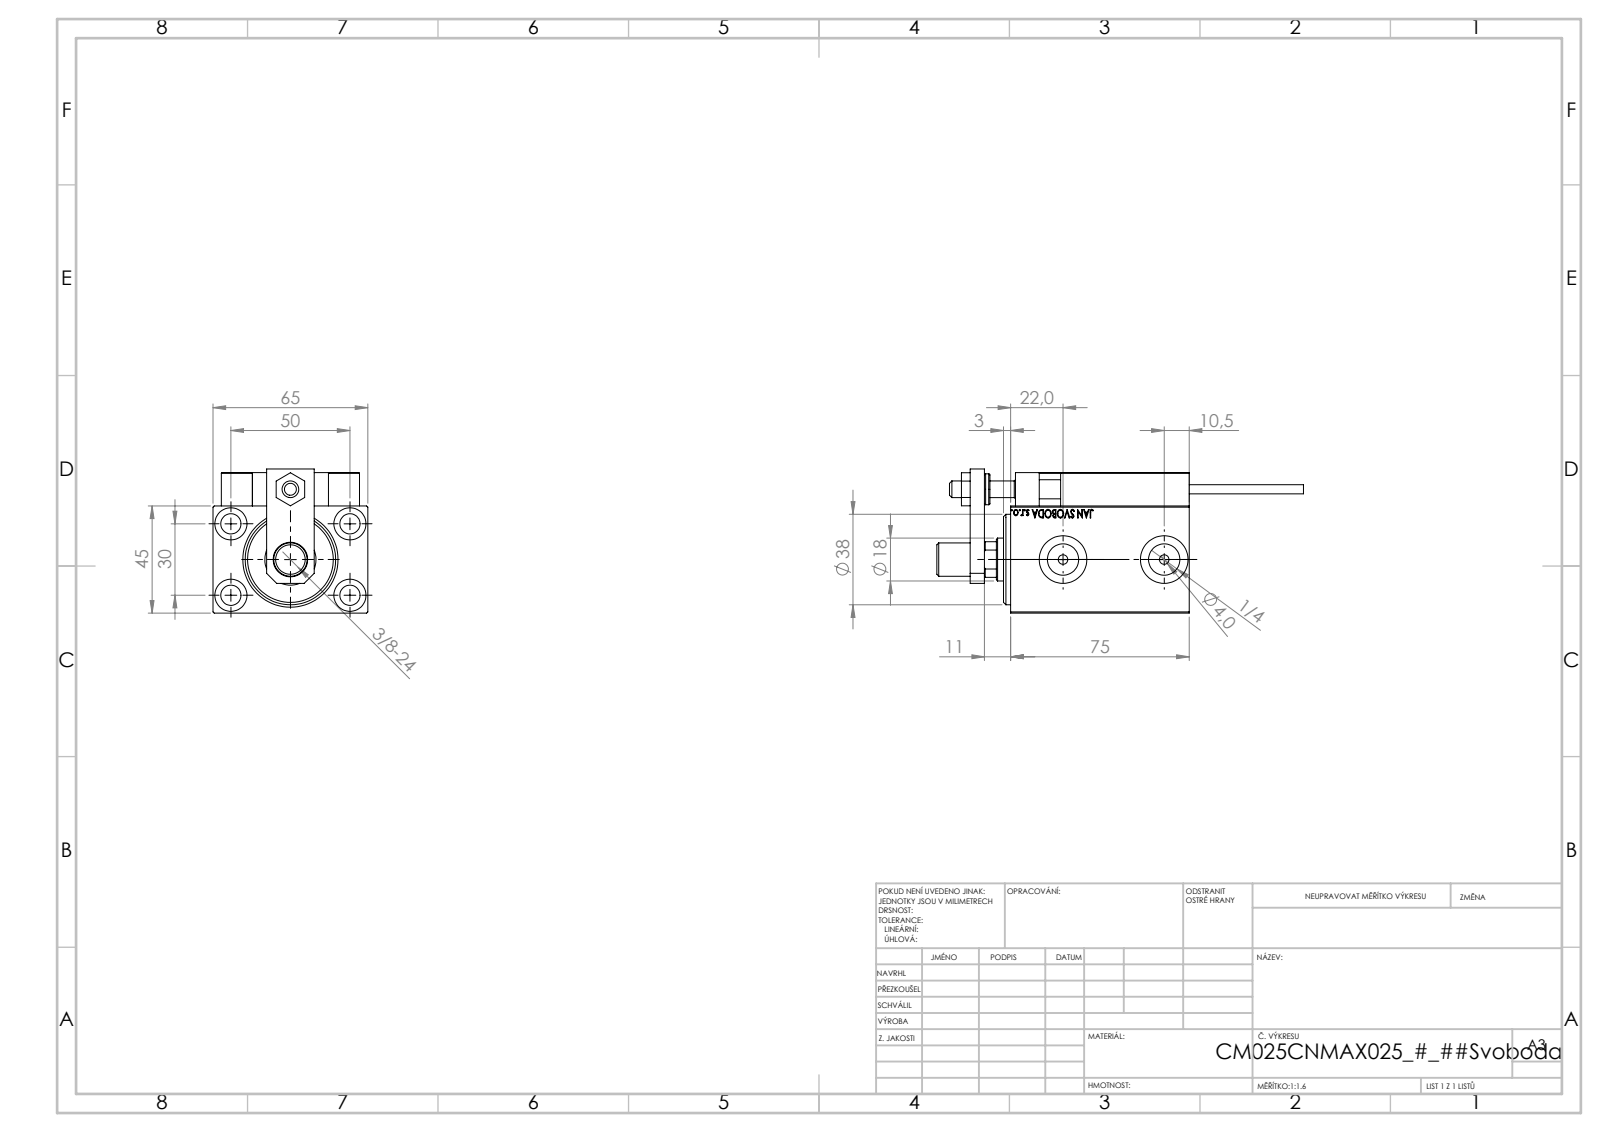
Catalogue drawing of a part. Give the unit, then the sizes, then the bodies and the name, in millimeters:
Units: millimetres
Overall size (bounding box): 154 × 65 × 60.5
Round holes (diameter × count): ⌀4 ×6, ⌀8 ×5, ⌀8.5 ×5, ⌀3.2 ×4, ⌀13.5 ×4, ⌀5 ×2, ⌀13.16 ×2, ⌀20 ×2, ⌀7 ×1, ⌀14.5 ×1, ⌀18 ×1, ⌀21.5 ×1
Round bosses / shafts (diameter × count): ⌀5 ×2, ⌀3.8 ×2, ⌀14 ×1, ⌀13 ×1, ⌀12 ×1, ⌀11 ×1
Partial cylindrical surfaces — rounded edges, fillets, slot ends (radius × count): R0.3 ×30, R3 ×2, R8.5 ×1
Main face-to-face distances: 45, 14, 65, 6, 59, 3, 19, 13, 20, 86
Hole centre spacings: 29.15, 11.37, 20, 27.07, 28.9, 29.59, 29.69, 30
Volume: 238 573 mm³ · Surface area: 72 805 mm²
Bodies: 24 solids, 1295 faces (563 planar, 192 cylindrical, 540 other)
Part name (STEP PRODUCT): MAGNET; Block; KONCOVKA; V450CM_MALE_METRIC (+7 more)
STEP written by: SolidWorks 2019 (CONFIG_CONTROL_DESIGN)
